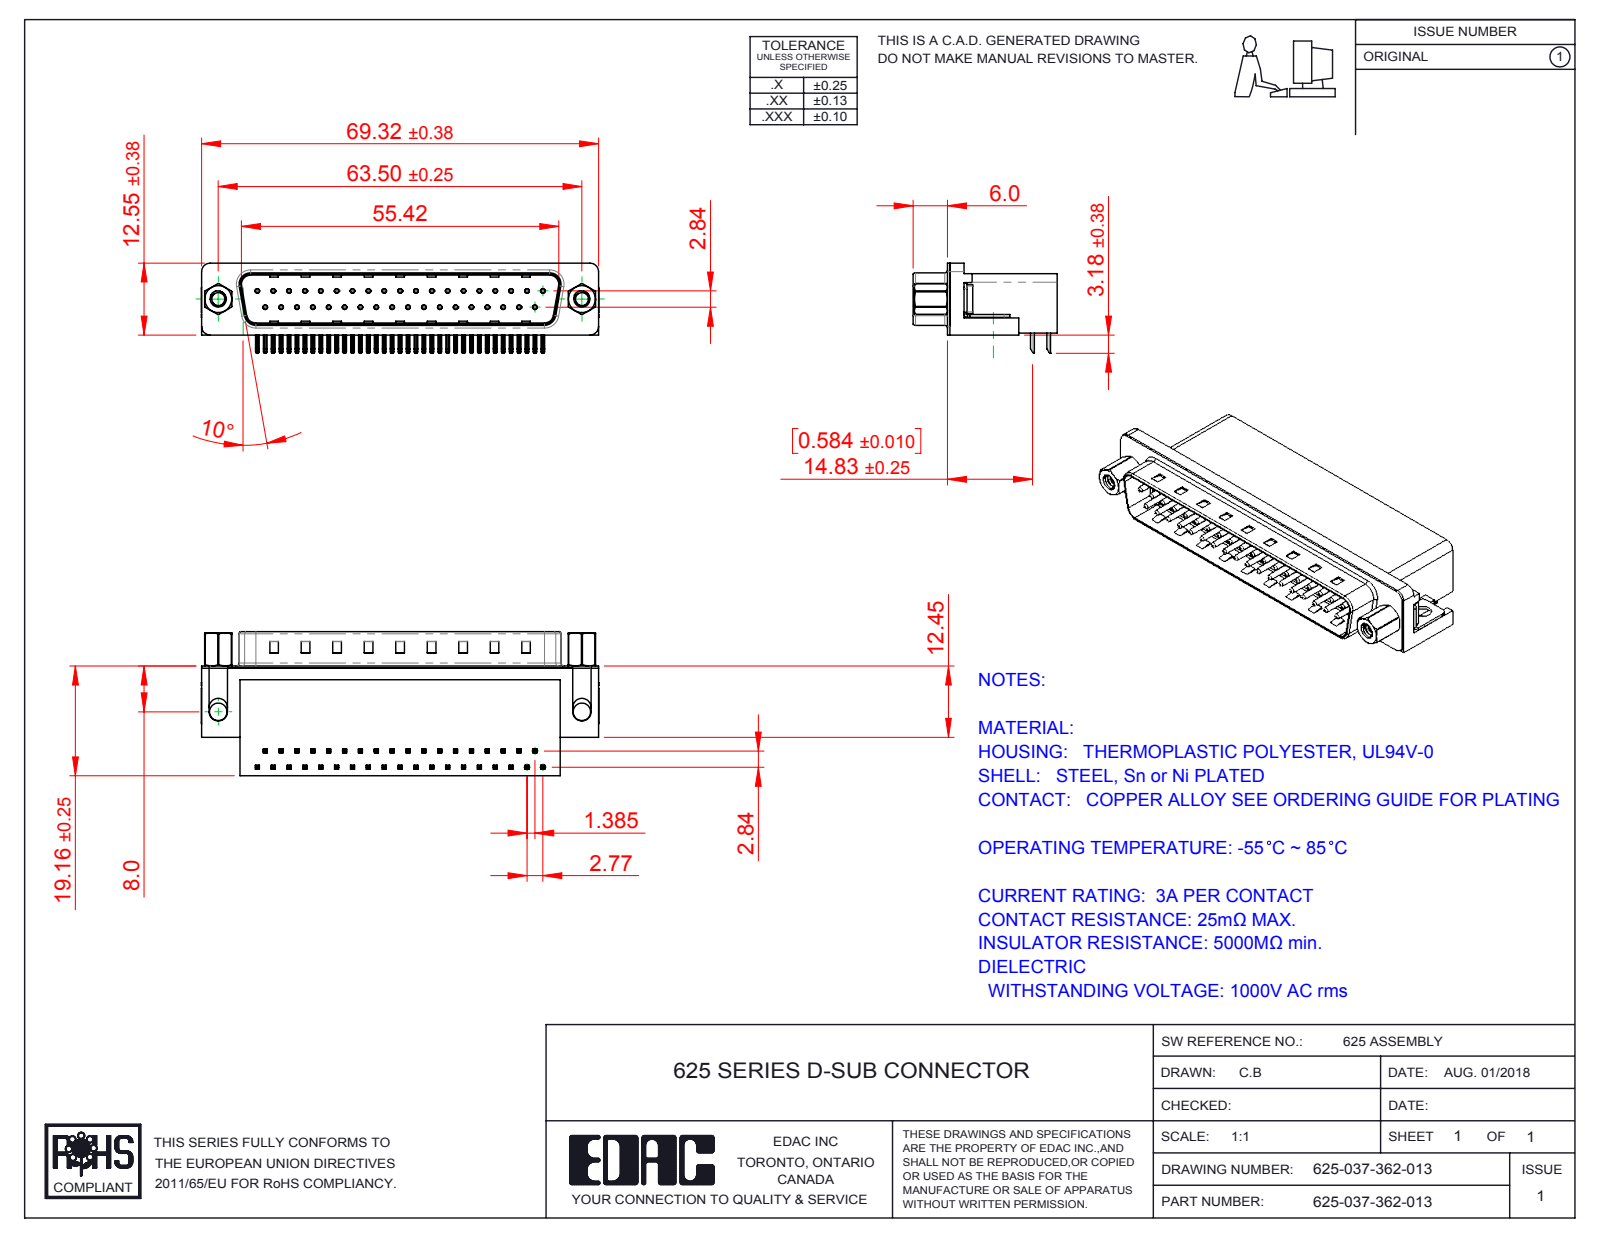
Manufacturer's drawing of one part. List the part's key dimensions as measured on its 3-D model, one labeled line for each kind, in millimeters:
Part name (STEP PRODUCT): 625 Contact Top; 625-037-362-013; 625 4-40 Threaded Rivet; 625 Thru Hole Board Mount (+4 more)
STEP written by: SolidWorks 2016 (CONFIG_CONTROL_DESIGN)
Units: millimetres
Bodies: 45 solids, 3327 faces (2035 planar, 989 cylindrical, 303 other)
Overall size (bounding box): 69.4 × 25.16 × 15.73
Volume: 12 812 mm³ · Surface area: 12 224 mm²
Round holes (diameter × count): ⌀0.35 ×37, ⌀0.8 ×37, ⌀2.26 ×2, ⌀2.29 ×2, ⌀3.05 ×2, ⌀4 ×2, ⌀4.8 ×2, ⌀5 ×2
Round bosses / shafts (diameter × count): ⌀0.75 ×37, ⌀4.9 ×2, ⌀4.75 ×2, ⌀3.9 ×2, ⌀2.79 ×2
Partial cylindrical surfaces — rounded edges, fillets, slot ends (radius × count): R0.25 ×156, R0.12 ×74, R1 ×16, R0.5 ×9, R1.6 ×8, R1.5 ×7, R0.9 ×4, R2 ×4
Main face-to-face distances: 10.34, 0.4, 18.76, 8.76, 19.16, 10.1, 2.84, 2.09, 1.74, 8.36
Hole centre spacings: 3.16, 2.77, 5.54, 8.31, 11.08, 13.85, 19.39, 22.16
